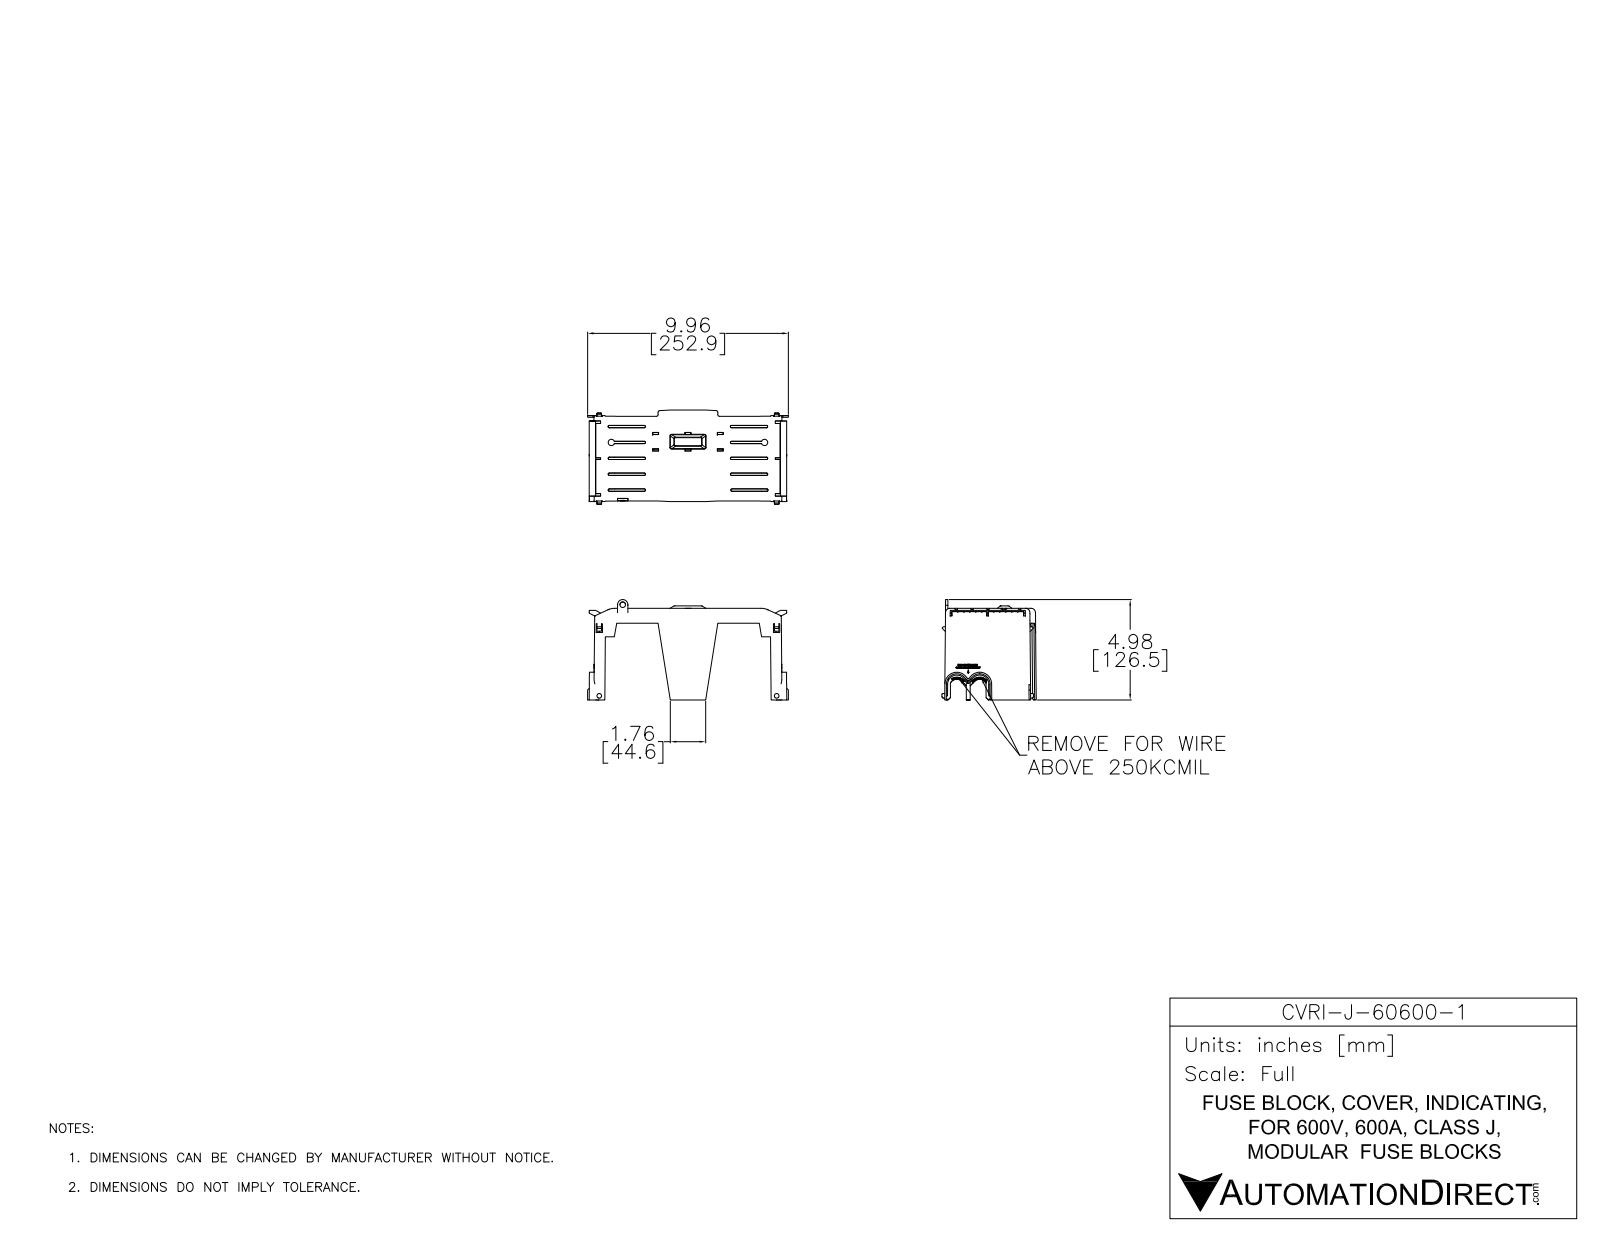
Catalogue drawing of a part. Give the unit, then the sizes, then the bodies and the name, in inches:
Units: inches
Overall size (bounding box): 9.959 × 4.983 × 4.677
Round holes (diameter × count): ⌀0.276 ×1
Partial cylindrical surfaces — rounded edges, fillets, slot ends (radius × count): R0.039 ×18, R0.118 ×12, R0.028 ×10, R0.217 ×9, R0.138 ×7, R0.079 ×6, R0.354 ×4, R0.512 ×4
Main face-to-face distances: 0.079, 0.079, 0.276, 0.197, 0.354, 0.803, 0.795, 0.118, 1.614, 0.158
Volume: 10.27 in³ · Surface area: 271.3 in²
Bodies: 1 solid, 2344 faces (1597 planar, 167 cylindrical, 580 other)
Part name (STEP PRODUCT): CVRI-J-60600-1
STEP written by: SolidWorks 2017 (AUTOMOTIVE_DESIGN)
